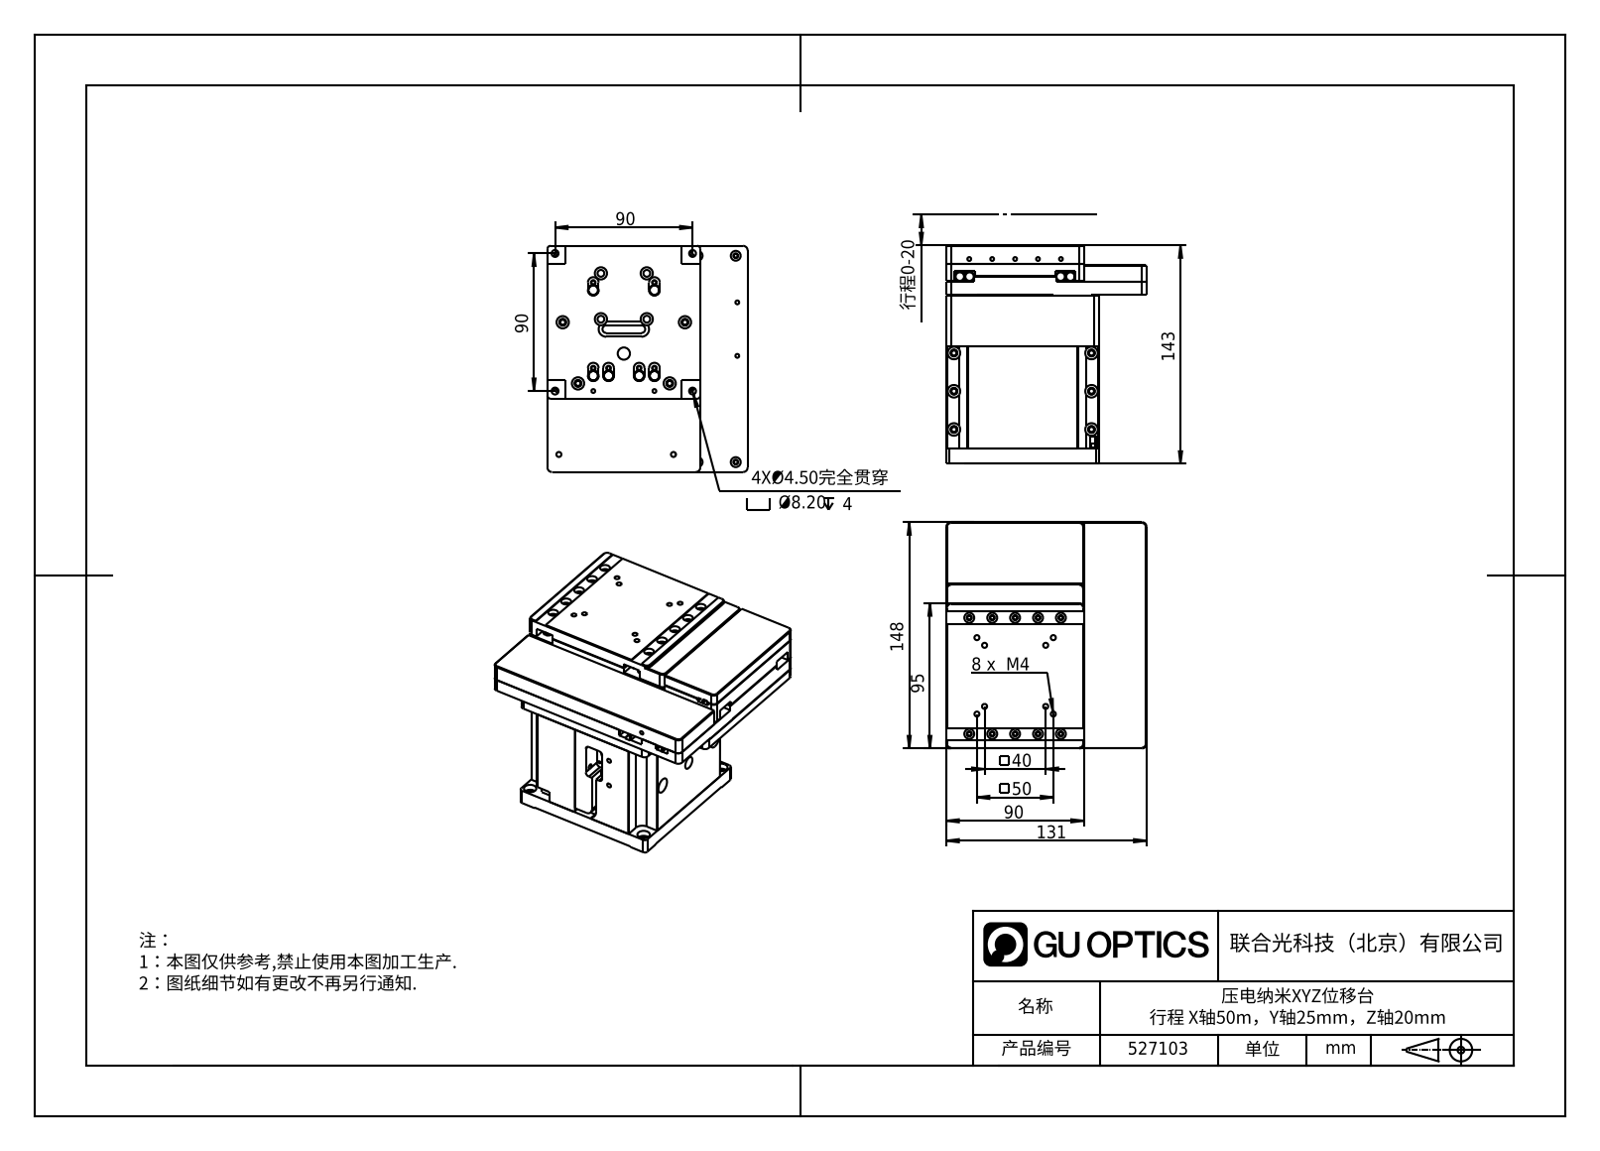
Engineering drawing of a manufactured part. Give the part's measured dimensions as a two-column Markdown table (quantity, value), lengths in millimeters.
| quantity | value |
| --- | --- |
| part name | VS4-1025TG+XY2-2550-20240620-cust |
| STEP written by | SolidWorks 2020 (CONFIG_CONTROL_DESIGN) |
| units | millimeters |
| bodies | 21 solids, 2729 faces (1587 planar, 793 cylindrical, 349 other) |
| overall size | 148 × 143 × 131 |
| volume | 1 049 000 mm³ |
| surface area | 347 417 mm² |
| round holes (diameter × count) | 3.2 × 54, 2.5 × 48, 2.55 × 48, 4.4 × 48, 6.5 × 36, 4.5 × 26, 3.3 × 24, 6 × 24, 8.25 × 14, 8 × 13, 1.6 × 11, 3 × 10 |
| round bosses / shafts (diameter × count) | 2 × 58, 5.6 × 8 |
| partial cylindrical surfaces (radius × count) | 2.5 × 89, 3 × 70, 2 × 24, 3.5 × 20, 1.5 × 18, 5 × 18, 0.5 × 14, 1 × 9 |
| main face-to-face distances | 0.5, 100, 3.5, 7, 15.5, 8.5, 9, 24, 6.5, 11.5 |
| hole center spacings | 15, 30, 16.55, 67.68, 45, 30.81, 72.5, 45.54 |
